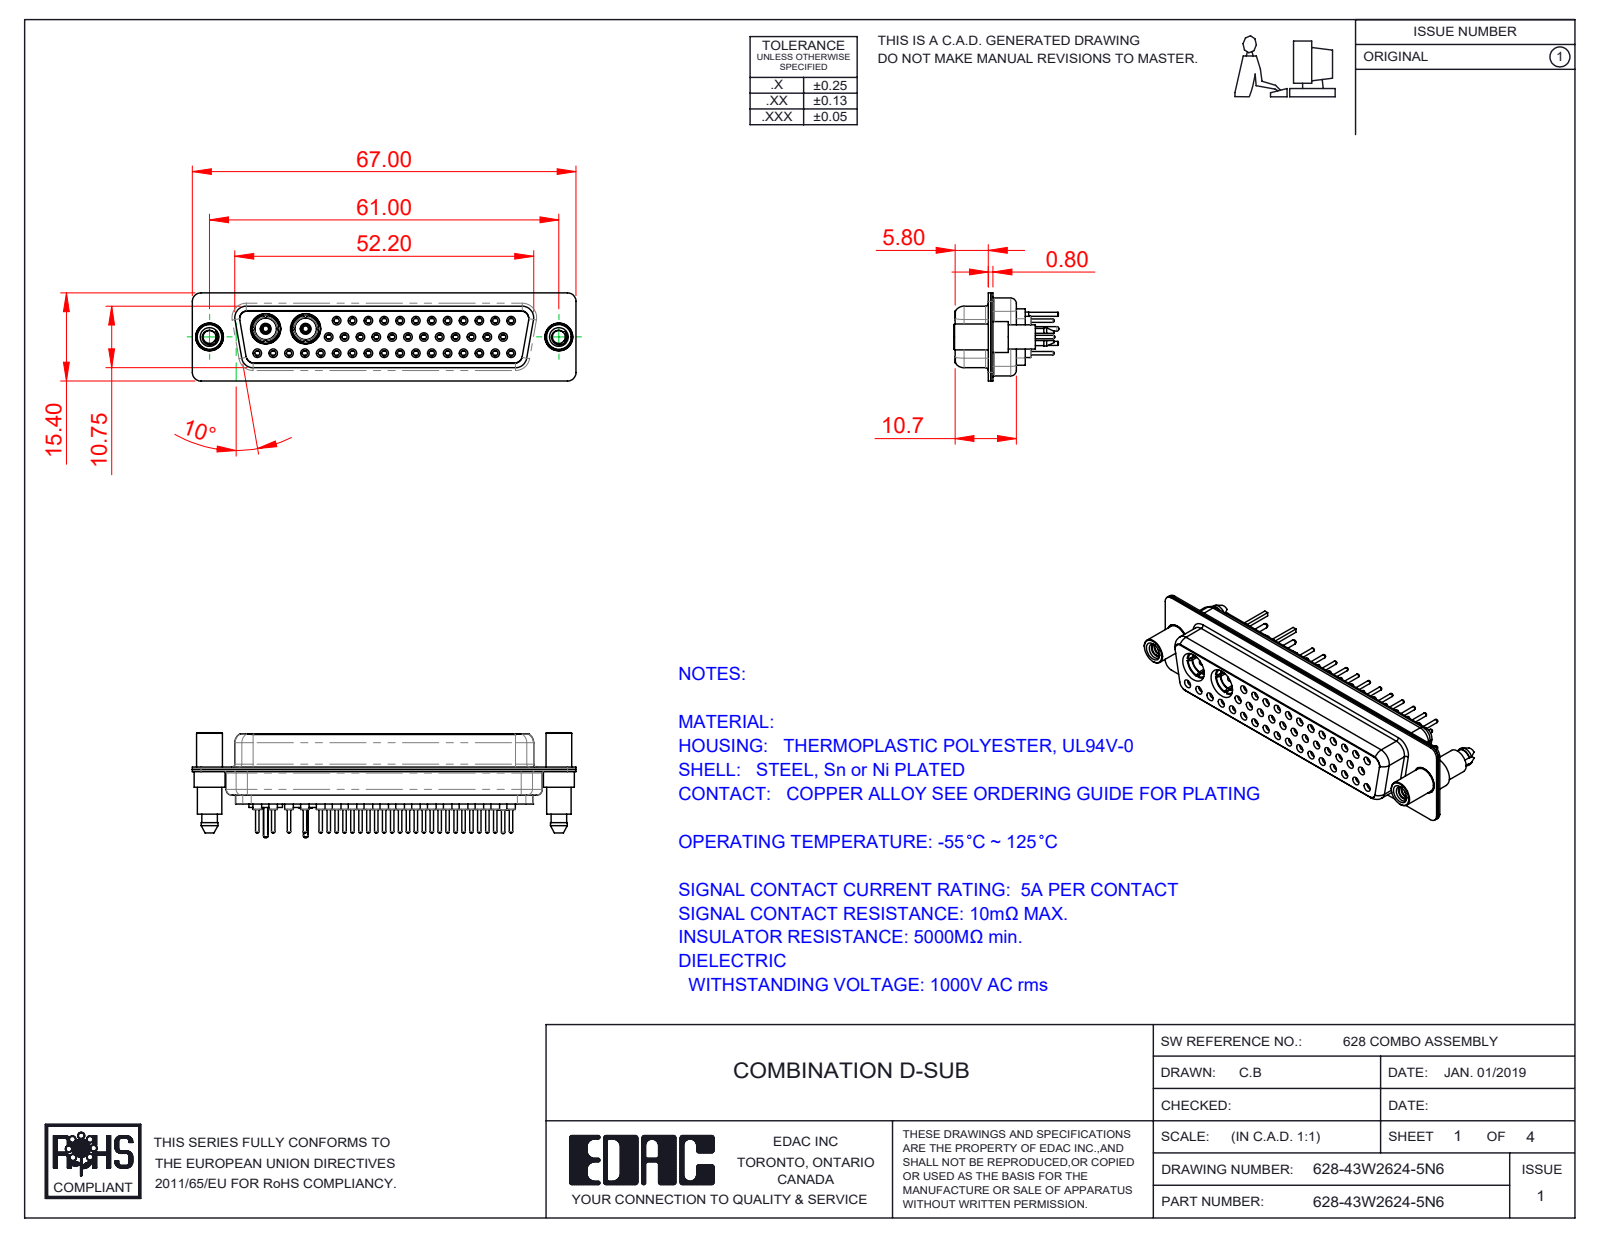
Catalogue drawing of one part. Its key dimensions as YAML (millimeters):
part_name: "Co-Ax Plug Assy_St; 628Combo Contact Row 1_24; 628Combo Housing_43W2; 628Combo Shell Rear_50 Contacts (+8 more)"
step_written_by: "SolidWorks 2016 (CONFIG_CONTROL_DESIGN)"
units: millimeters
bodies: {solids: 54, faces: 2840, planar: 814, cylindrical: 1034, other: 992}
overall_size: [67, 18.35, 15.4]
volume: 7269
surface_area: 15449
round_holes:
  - {diameter: 1.1, count: 43}
  - {diameter: 1.5, count: 43}
  - {diameter: 0.9, count: 41}
  - {diameter: 2, count: 41}
  - {diameter: 1.6, count: 29}
  - {diameter: 1.7, count: 12}
  - {diameter: 4.85, count: 4}
  - {diameter: 2.26, count: 2}
  - {diameter: 2.83, count: 2}
  - {diameter: 3.3, count: 2}
  - {diameter: 3.92, count: 2}
  - {diameter: 4, count: 2}
round_bosses_or_shafts:
  - {diameter: 2.2, count: 41}
  - {diameter: 0.6, count: 41}
  - {diameter: 1.6, count: 12}
  - {diameter: 5.85, count: 2}
  - {diameter: 5.4, count: 2}
  - {diameter: 5.2, count: 2}
  - {diameter: 5, count: 2}
  - {diameter: 4.95, count: 2}
partial_cylinders:
  - {radius: 1.5, count: 18}
  - {radius: 1.35, count: 12}
  - {radius: 2, count: 12}
  - {radius: 1.6, count: 10}
  - {radius: 0.25, count: 4}
  - {radius: 0.5, count: 4}
  - {radius: 0.6, count: 4}
  - {radius: 0.65, count: 4}
face_to_face_distances: [0.4, 6.05, 11.33, 6.45, 1.87, 10.35, 10.93, 12.25, 6.2, 5.8]
hole_center_spacings: [2.77, 3.16, 5.54, 8.31, 11.08, 13.85, 16.62, 19.39]
